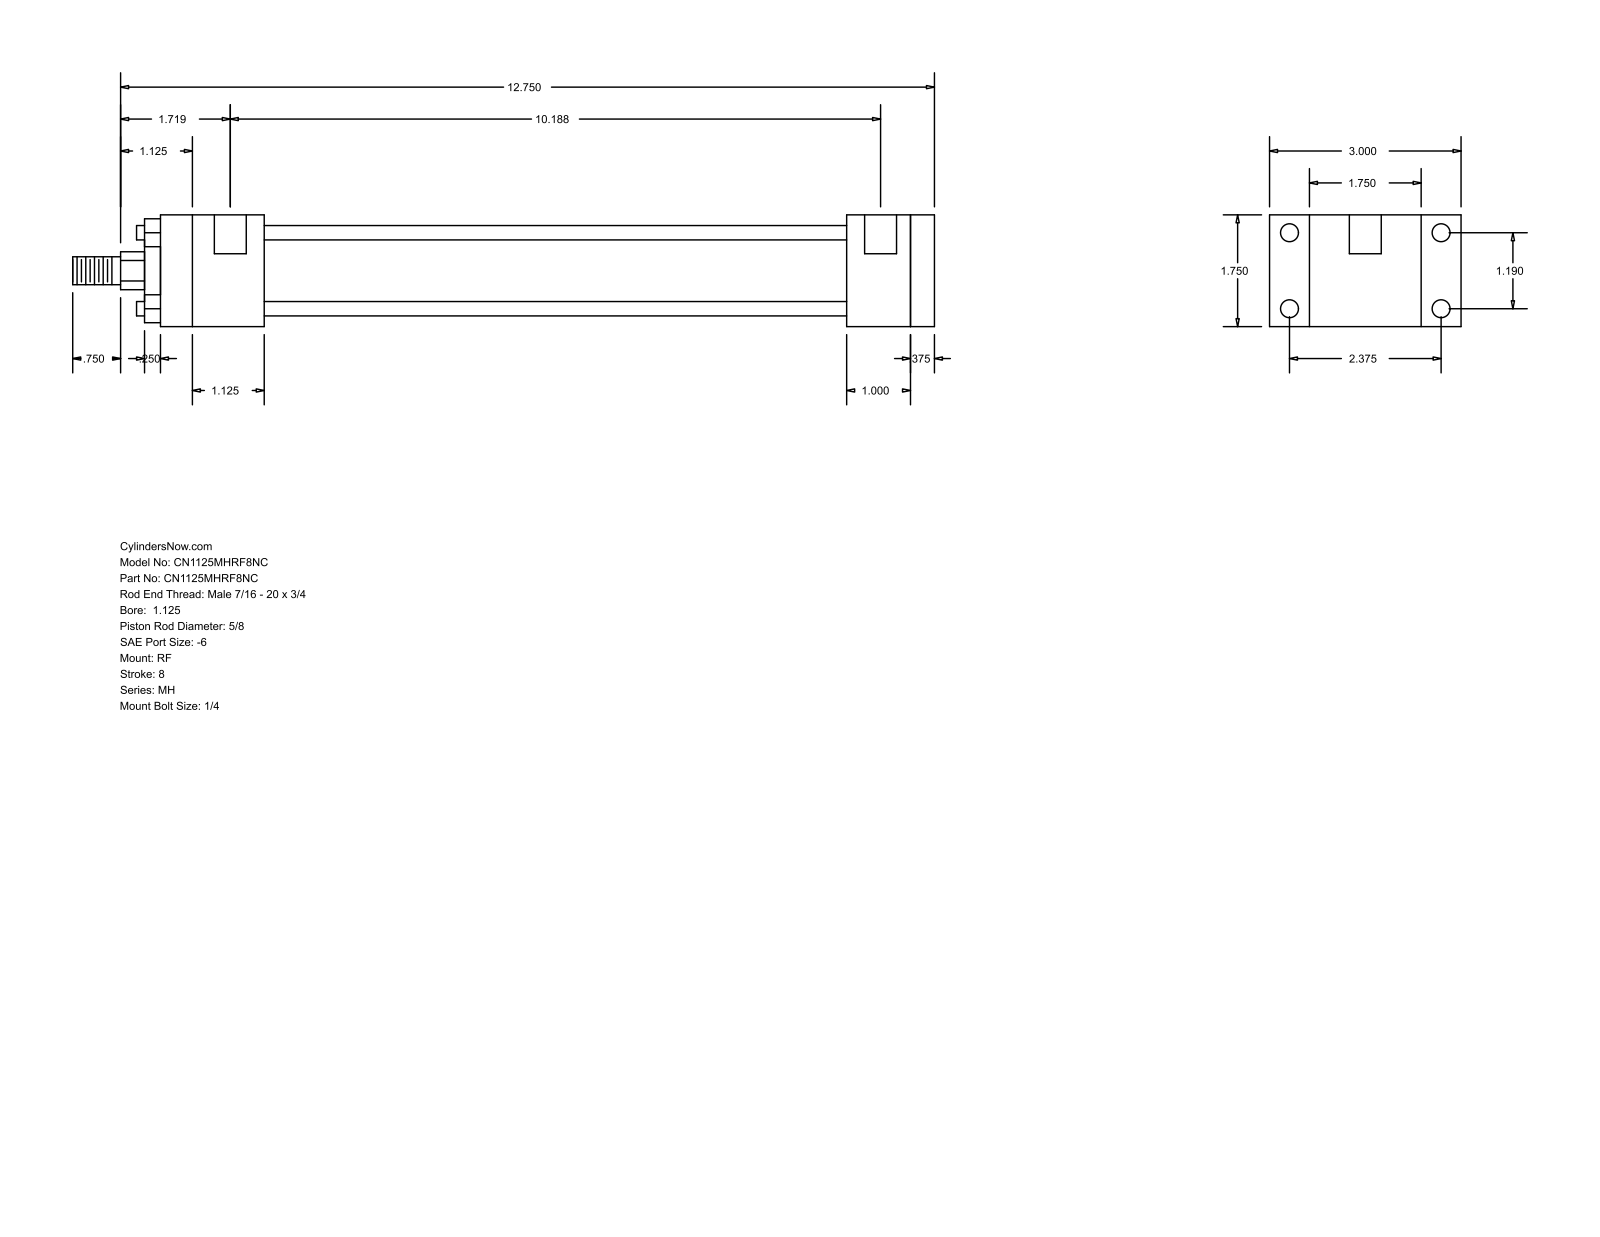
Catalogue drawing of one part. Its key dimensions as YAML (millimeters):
part_name: "MH_RF__0112_0.625"
step_written_by: "GSSL Pune (CONFIG_CONTROL_DESIGN)"
units: millimeters
bodies: {solids: 0, faces: 92, planar: 64, cylindrical: 28, other: 0}
overall_size: [342.9, 76.2, 44.45]
round_holes:
  - {diameter: 5.56, count: 4}
  - {diameter: 7.14, count: 4}
  - {diameter: 12.7, count: 2}
round_bosses_or_shafts:
  - {diameter: 5.71, count: 4}
  - {diameter: 34.92, count: 1}
  - {diameter: 28.57, count: 1}
  - {diameter: 15.88, count: 1}
  - {diameter: 11.11, count: 1}
partial_cylinders:
  - {radius: 7.54, count: 1}
face_to_face_distances: [44.46, 9.53, 307.97, 15.87, 257.17, 266.7, 231.78, 25.39, 34.92, 41.27]
hole_center_spacings: [30.22, 60.32, 67.47, 255.59, 3.17, 258.76]
